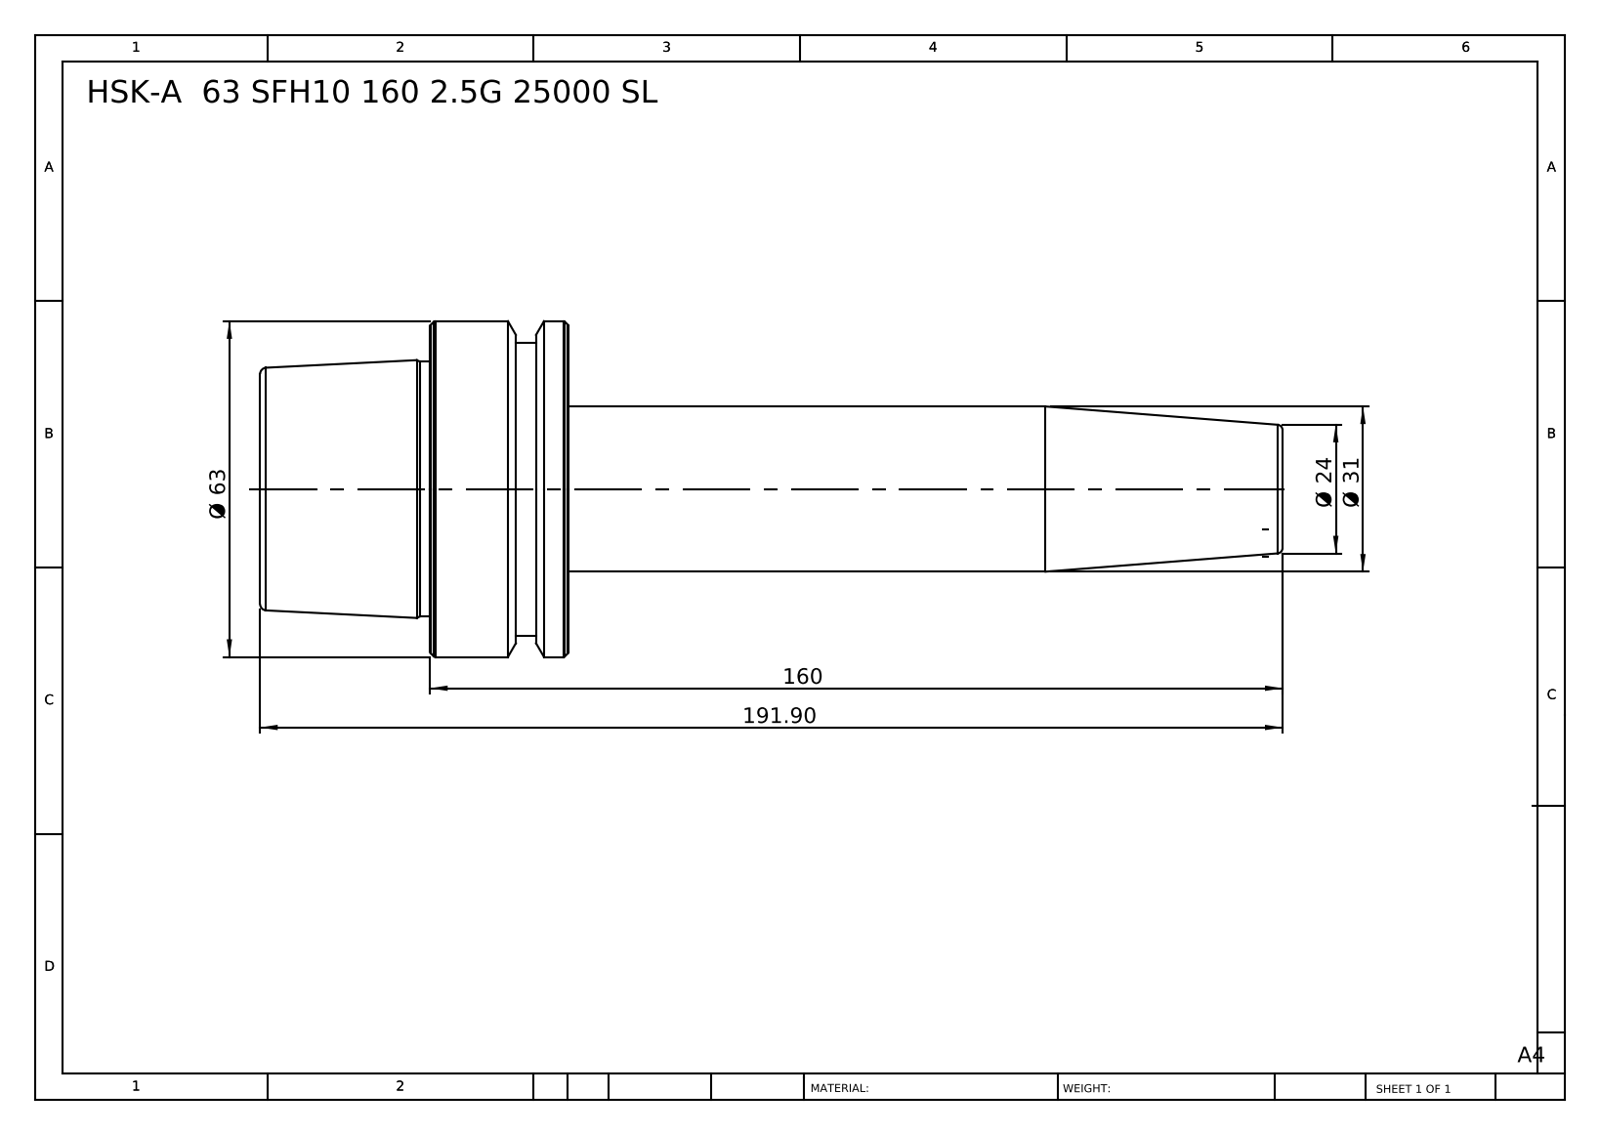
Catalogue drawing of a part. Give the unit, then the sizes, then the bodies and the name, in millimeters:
Units: millimetres
Overall size (bounding box): 191.9 × 63 × 63
Round bosses / shafts (diameter × count): ⌀63 ×1, ⌀55 ×1, ⌀47.78 ×1, ⌀31 ×1
Main face-to-face distances: 57.9, 26, 31.9, 134, 160, 191.9, 140.1, 6.1, 19.9, 51.8
Volume: 226 713 mm³ · Surface area: 28 892 mm²
Bodies: 1 solid, 46 faces (6 planar, 10 cylindrical, 30 other)
Part name (STEP PRODUCT): HSK-A 63 SFH10 160 2.5G 25000 SL
STEP written by: SolidWorks 2014 (CONFIG_CONTROL_DESIGN)
